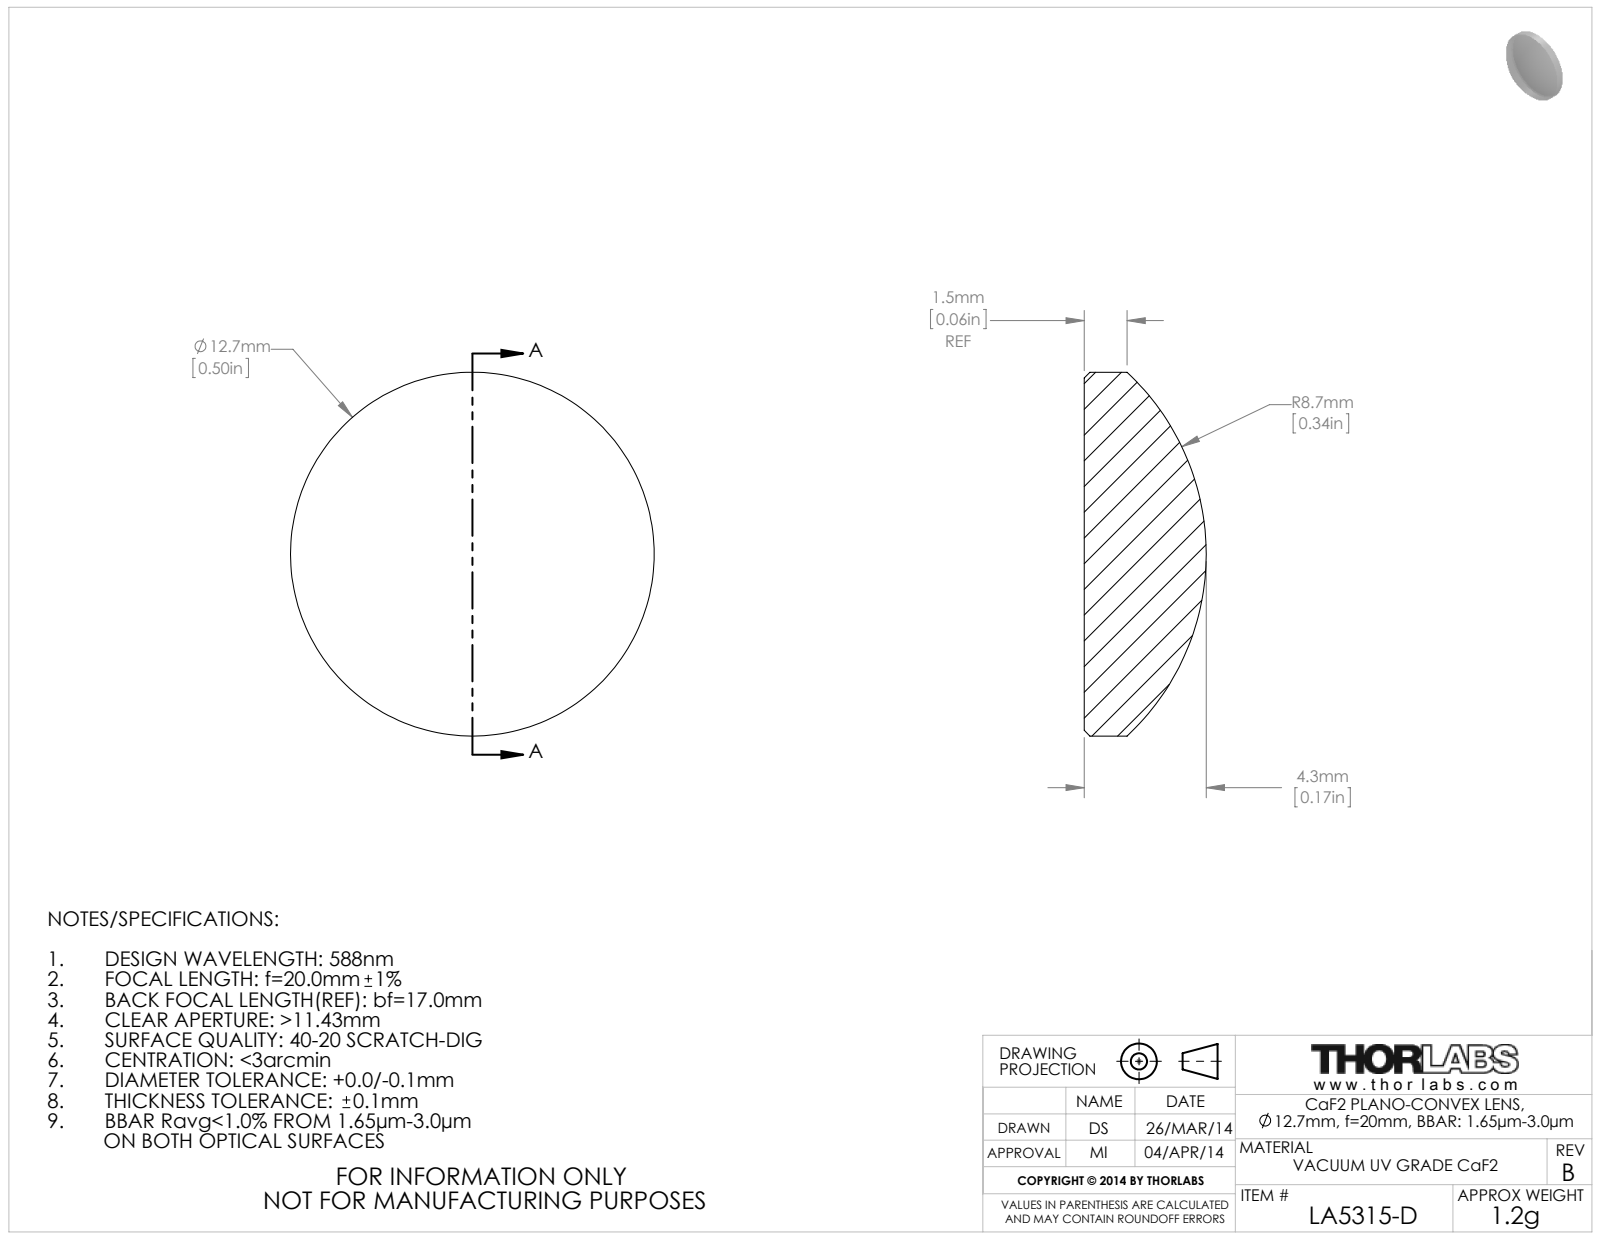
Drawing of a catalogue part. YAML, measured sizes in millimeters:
part_name: "22969-E0W"
step_written_by: "SolidWorks 2011 (AUTOMOTIVE_DESIGN)"
units: millimeters
bodies: {solids: 0, faces: 5, planar: 1, cylindrical: 2, other: 2}
overall_size: [12.7, 12.7, 4.26]
round_bosses_or_shafts:
  - {diameter: 12.7, count: 1}
